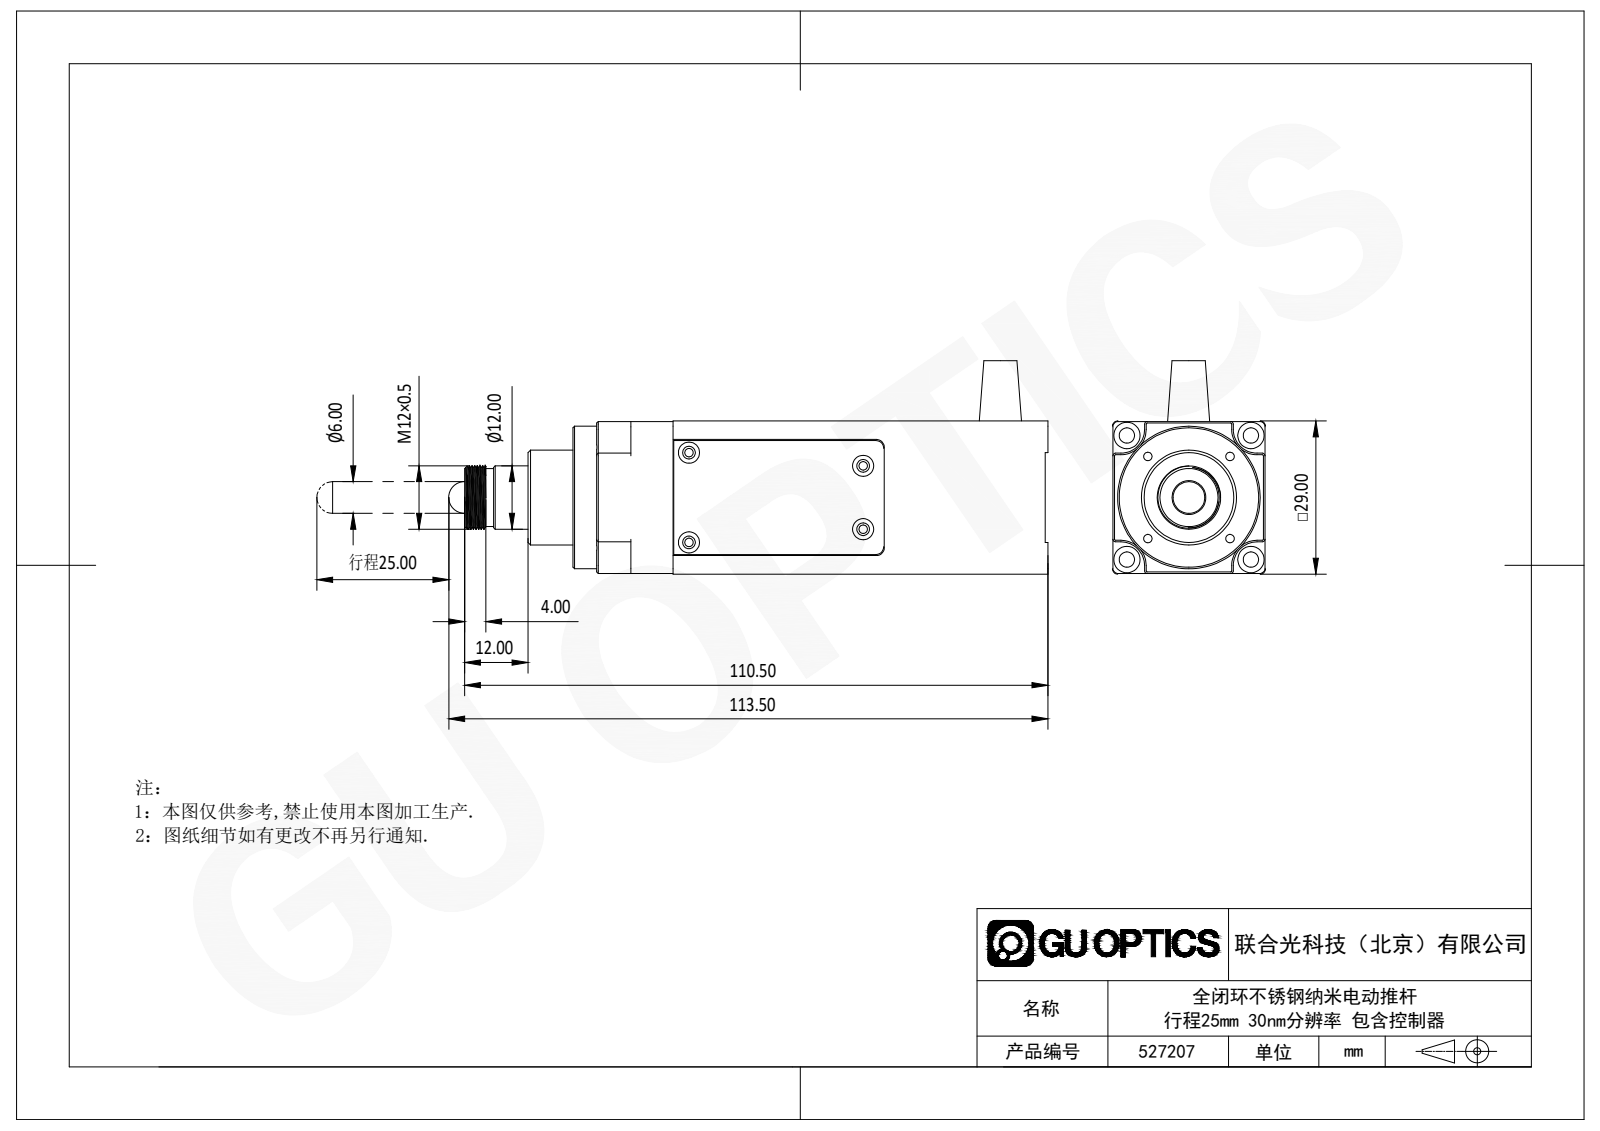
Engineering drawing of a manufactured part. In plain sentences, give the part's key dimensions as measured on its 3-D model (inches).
The part is named "527207". Its 3-D file was written by "SolidWorks 2020 (CONFIG_CONTROL_DESIGN)". It is 0 solids with 379 faces: 136 planar, 183 cylindrical and 60 other. Overall it measures 4.469 by 1.591 by 1.142 inches. Round holes: 4 of diameter 0.197, 1 of diameter 0.039, 1 of diameter 0.433, 1 of diameter 0.472, 1 of diameter 0.709, 1 of diameter 1.063. Round bosses or shafts: 12 of diameter 0.063, 10 of diameter 0.098, 8 of diameter 0.157, 8 of diameter 0.094, 4 of diameter 0.197, 1 of diameter 0.252, 1 of diameter 0.236. Partial cylindrical surfaces (rounded edges, fillets, slot ends): 10 of radius 0.059, 8 of radius 0.02, 8 of radius 0.039, 4 of radius 0.079, 4 of radius 0.177. The main face-to-face distances are 1.138, 1.142, 1.134, 1.083, 0.059, 1.079, 0.055, 2.776, 0.177, 0.236. The hole center spacings are 0.997, 1.054, 1.971, 2.05, 0.472, 0.669.
